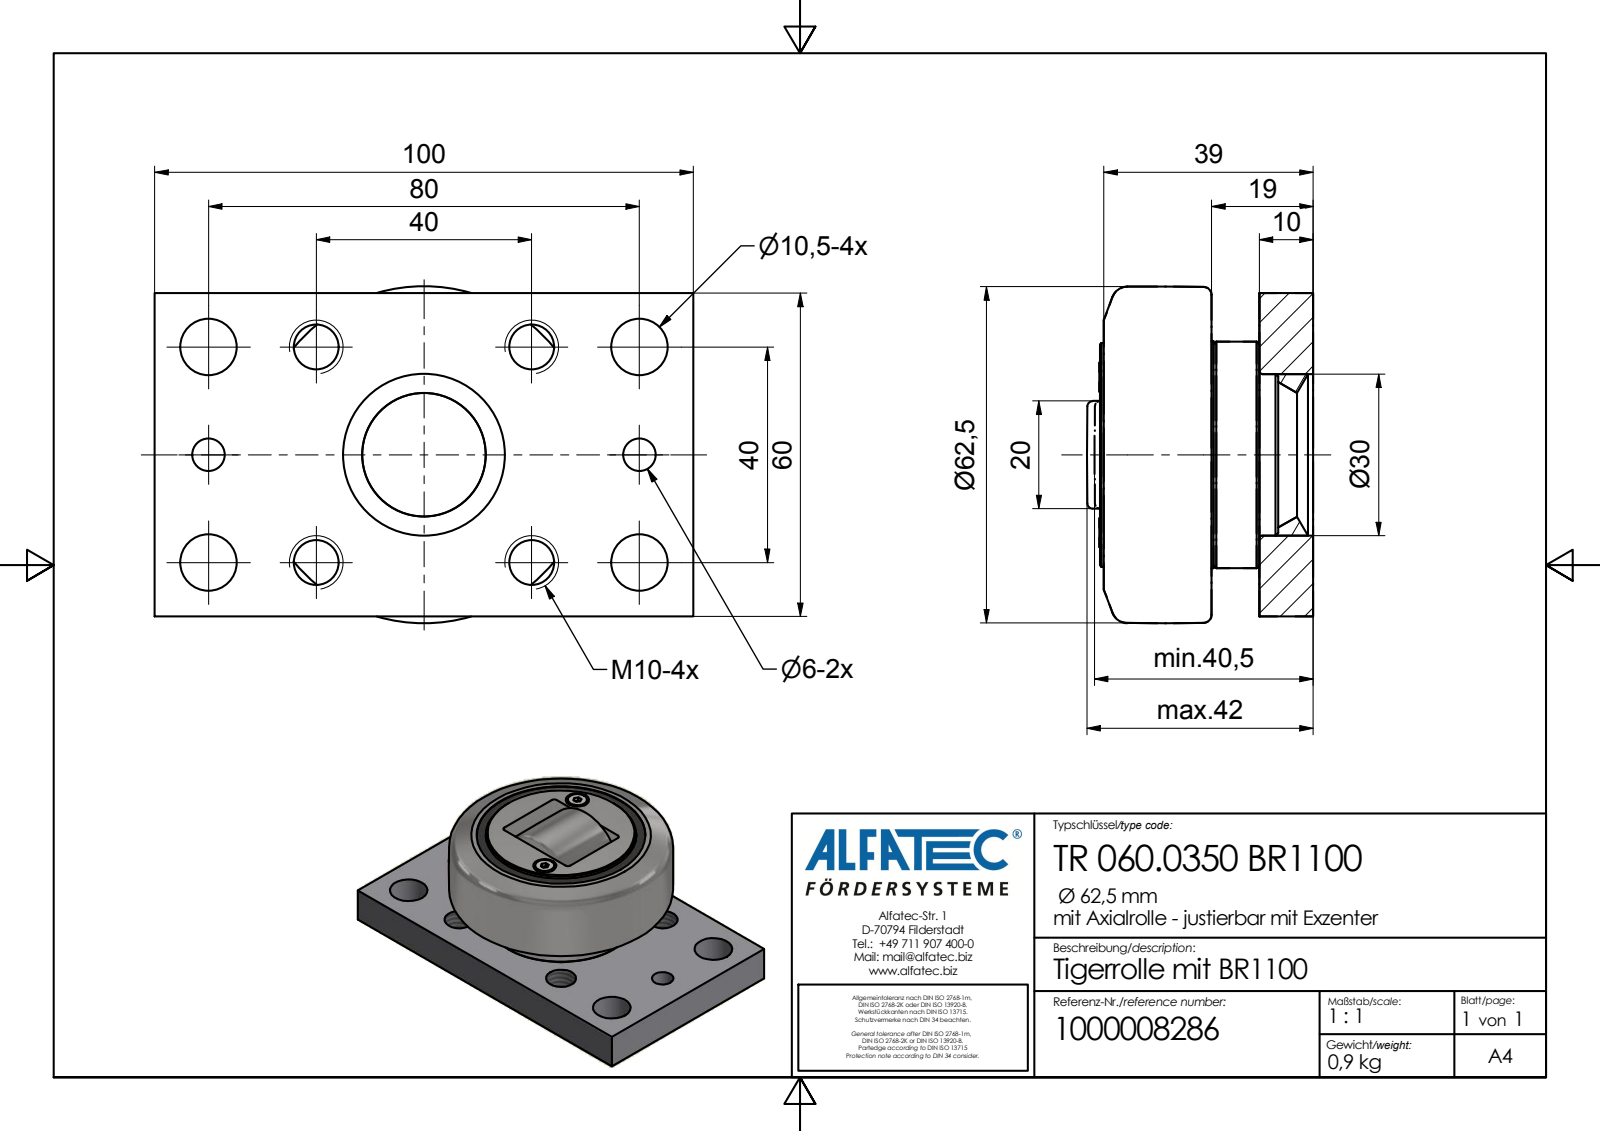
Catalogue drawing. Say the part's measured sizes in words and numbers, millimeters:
The part is named "TR 060.0350 BR1100_Kontur". Its 3-D file was written by "Autodesk Inventor 2020 (AP242_MANAGED_MODEL_BASED_3D_ENGINEERING_MIM_LF)". It is 1 solid with 281 faces: 160 planar, 96 cylindrical and 25 other. Overall it measures 100 by 62.5 by 42 millimeters. Its volume is 120 132 cubic millimeters and its surface area 32 633 square millimeters. Round holes: 4 of diameter 8.38, 4 of diameter 10.5, 2 of diameter 3.4, 2 of diameter 6, 1 of diameter 13.4, 1 of diameter 17, 1 of diameter 30, 1 of diameter 38, 1 of diameter 42, 1 of diameter 42.97, 1 of diameter 47. Round bosses or shafts: 2 of diameter 5.35, 2 of diameter 3, 1 of diameter 42.1, 1 of diameter 41.5, 1 of diameter 15. Partial cylindrical surfaces (rounded edges, fillets, slot ends): 8 of radius 1, 2 of radius 8.11, 1 of radius 5, 1 of radius 14.25. The main face-to-face distances are 10, 20, 18.85, 8.85, 60, 18.75, 1.25, 20.75, 39.6, 29.6. The hole center spacings are 20, 28.28, 40, 44.72, 60, 63.25, 72.11, 82.46.
